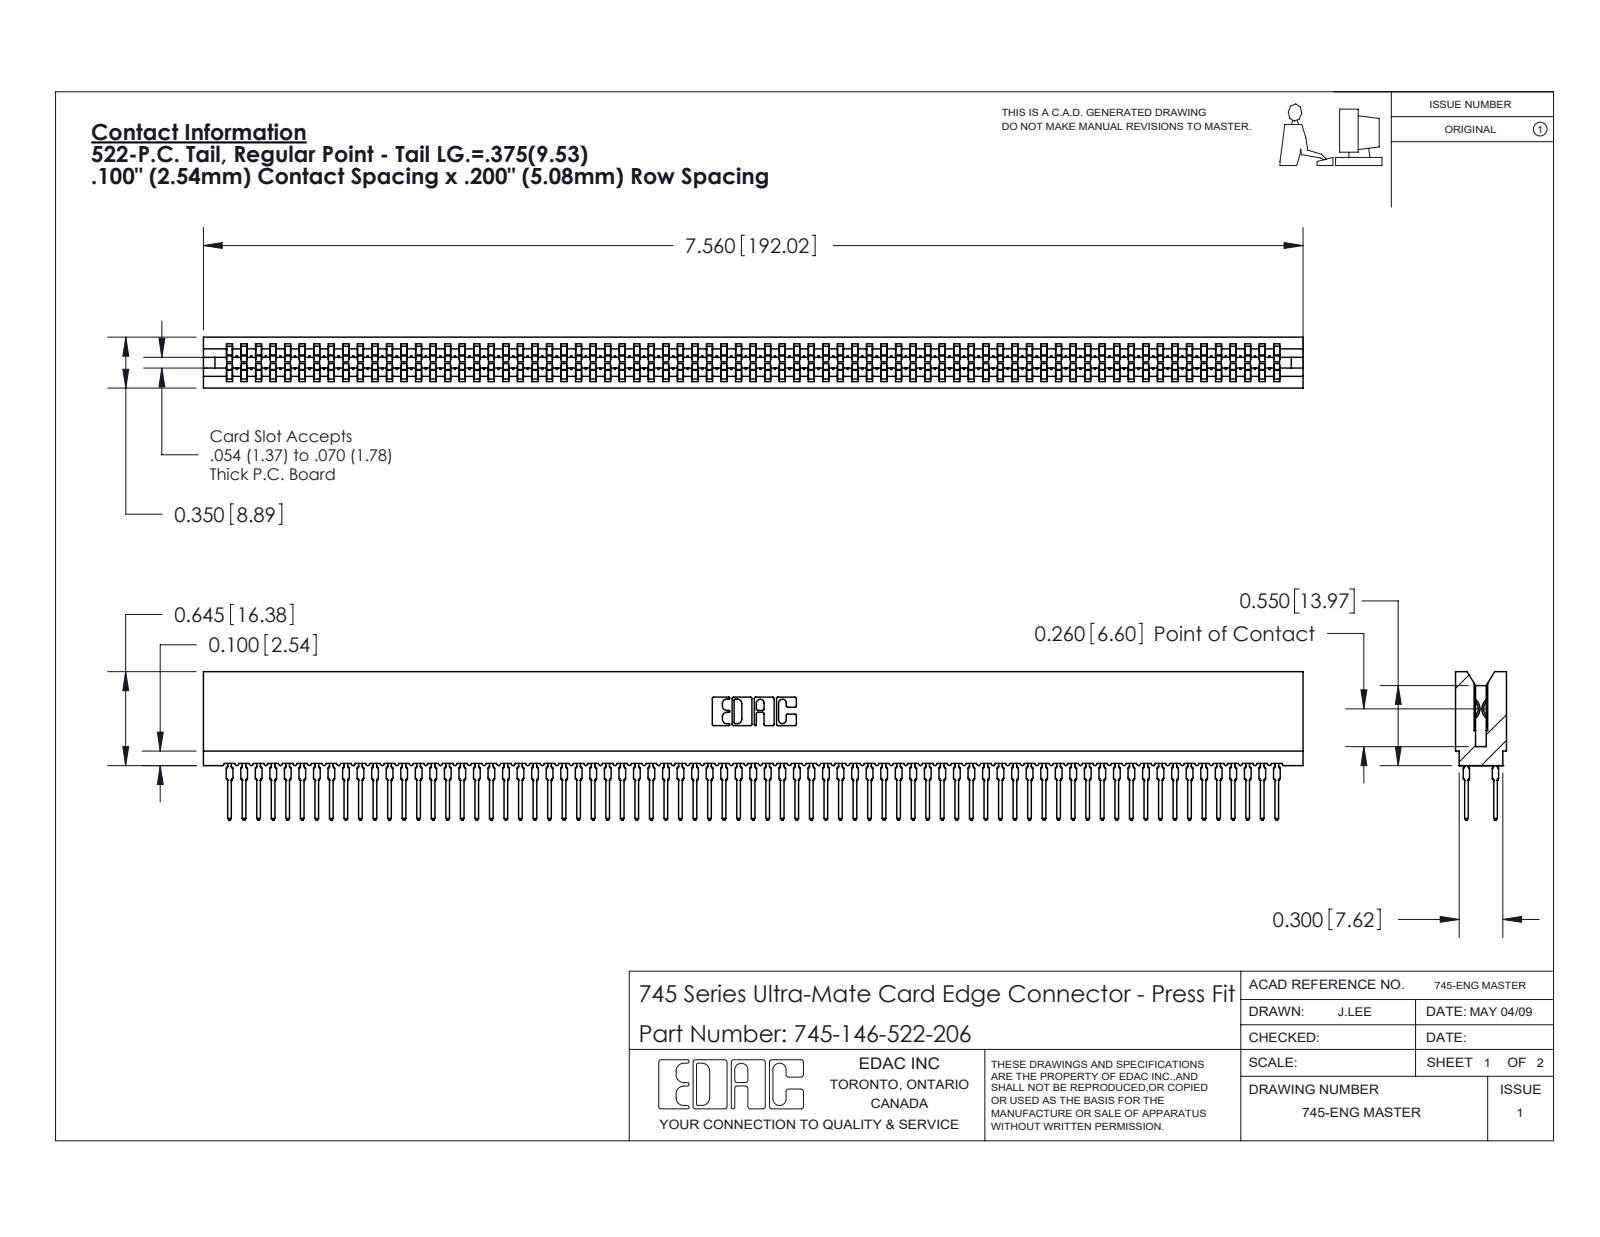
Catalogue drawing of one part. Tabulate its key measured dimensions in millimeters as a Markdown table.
| quantity | value |
| --- | --- |
| part name | 745 Part_Insulator Option - 06; 745-146-522-206; 745-292-001_522 |
| STEP written by | SolidWorks 2020 (CONFIG_CONTROL_DESIGN) |
| units | millimeters |
| bodies | 147 solids, 13163 faces (6772 planar, 2595 cylindrical, 3796 other) |
| overall size | 192 × 25.9 × 8.9 |
| volume | 17 240 mm³ |
| surface area | 36 300 mm² |
| partial cylindrical surfaces (radius × count) | 0.5 × 292, 0.4 × 146, 0.3 × 22, 0.1 × 8, 0.3 × 8, 0.2 × 6, 0.8 × 6, 0.7 × 3 |
| main face-to-face distances | 8.9, 1.6, 7.3, 1.1, 7.7, 0.5, 6.2, 3.5, 5.4, 2.4 |
